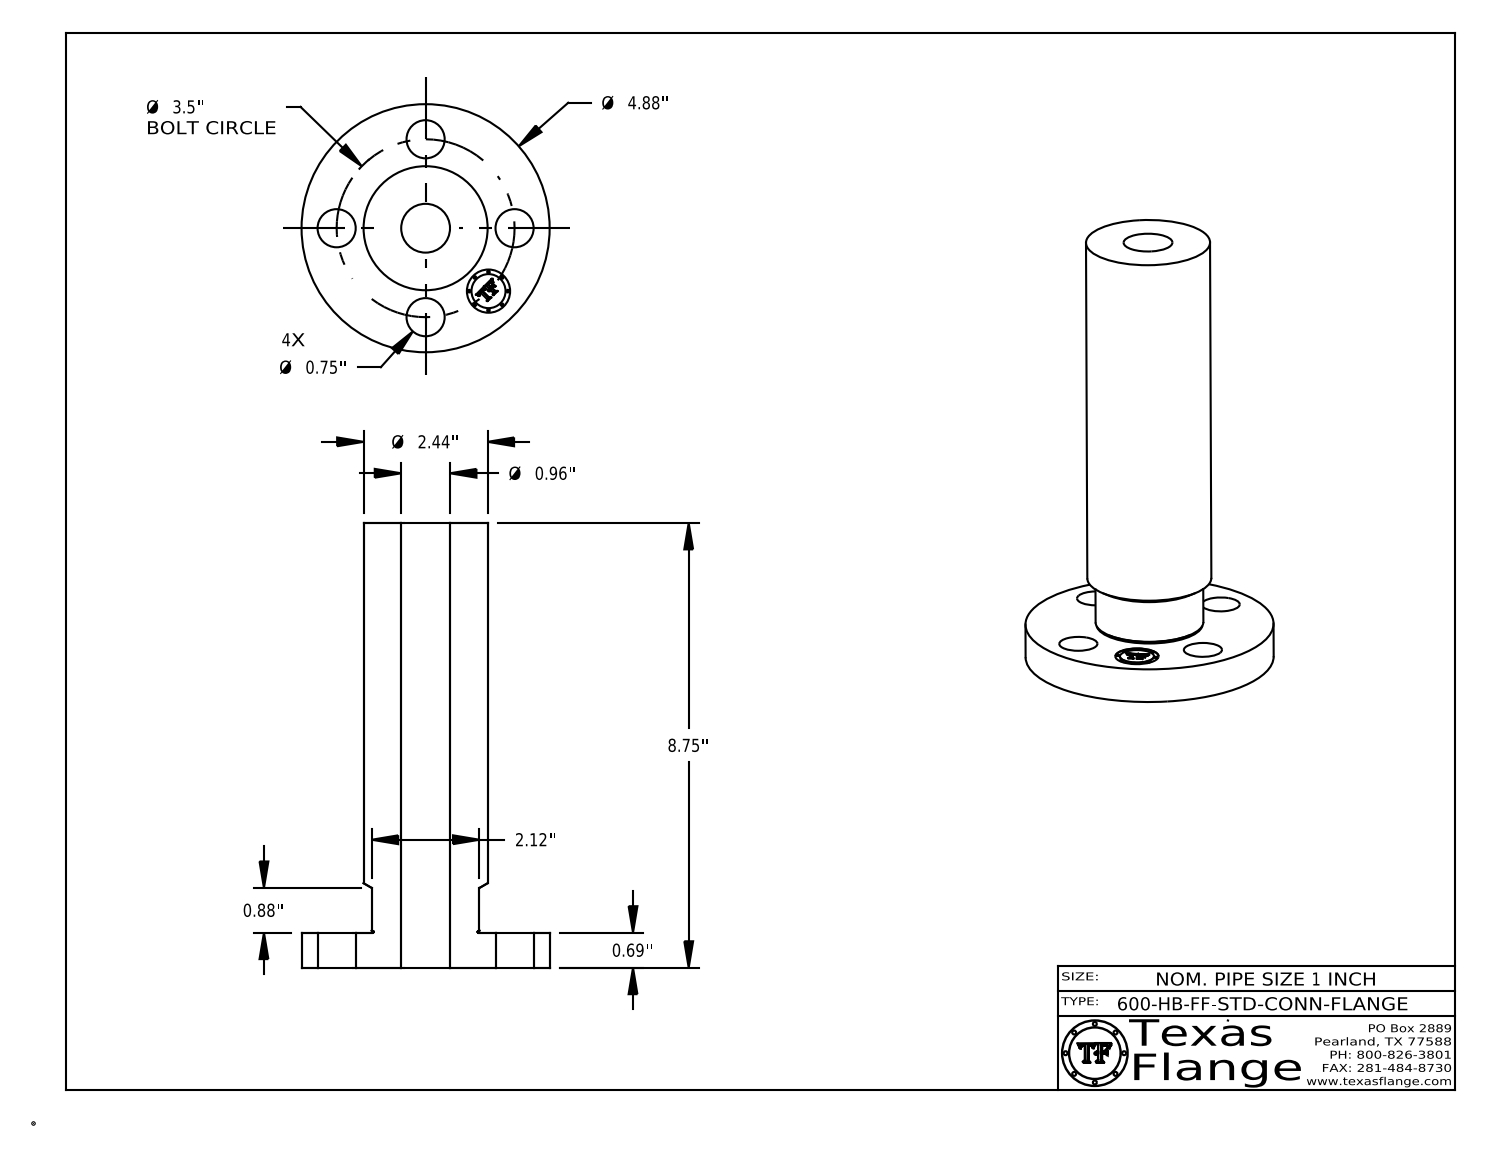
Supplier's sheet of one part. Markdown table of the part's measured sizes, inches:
| quantity | value |
| --- | --- |
| part name | 1-600-HB-FF-STD-CONN-FLANGE |
| STEP written by | CATIA V5 STEP AP214 (AUTOMOTIVE_DESIGN) |
| units | inches |
| bodies | 1 solid, 410 faces (368 planar, 36 cylindrical, 6 other) |
| overall size | 8.75 × 4.88 × 4.88 |
| volume | 41.97 in³ |
| surface area | 138.9 in² |
| round holes (diameter × count) | 0.75 × 4, 0.85 × 1, 0.96 × 1 |
| round bosses / shafts (diameter × count) | 0.051 × 8, 4.88 × 1, 2.44 × 1, 2.12 × 1, 0.67 × 1 |
| main face-to-face distances | 0.69, 8.75, 8.06, 0.685, 8.065, 0.016, 0.254, 0.249, 0.046, 0.165 |
| hole center spacings | 1.75, 2.475, 1.339, 3.233, 3.5 |
